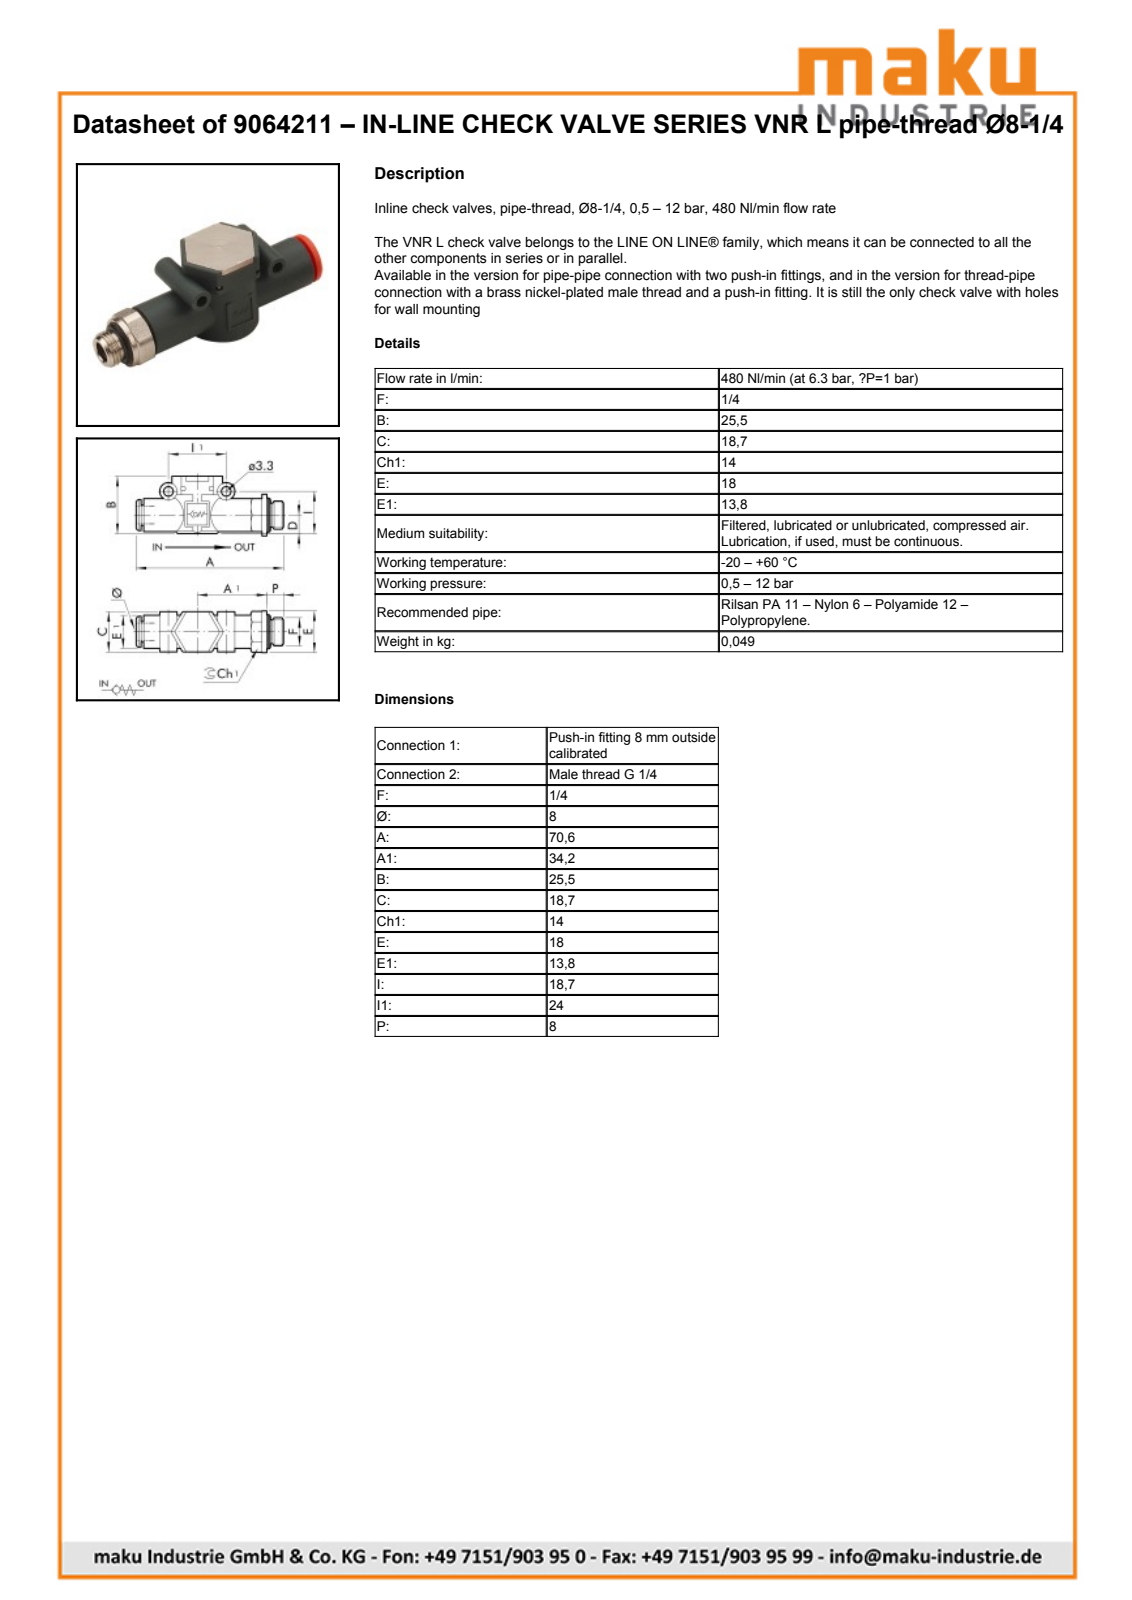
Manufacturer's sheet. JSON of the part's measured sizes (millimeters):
{"part_name": "9064211; LINE-ON-LINE D8 VSR-L body; LINE-ON-LINE D8-1/4 thread port; LINE-ON-LINE D8 VNR-L bushing (+1 more)", "step_written_by": "PARTsolutions (AUTOMOTIVE_DESIGN)", "units": "millimeters", "bodies": {"solids": 4, "faces": 148, "planar": 86, "cylindrical": 51, "other": 11}, "overall_size": [70.8, 26, 18.7], "volume_mm3": 9782, "surface_area_mm2": 10088, "round_holes": [[3.3, 2], [6, 2], [5.5, 1], [8, 1], [8.1, 1], [9.4, 1], [11, 1], [11.66, 1], [12.5, 1], [15, 1]], "round_bosses_or_shafts": [[6, 2], [18.8, 1], [18, 1], [13.8, 1], [13.6, 1], [13.16, 1], [11.1, 1], [10, 1]], "partial_cylinders_radius": [[3.75, 1], [7.95, 1], [10.2, 1], [10.35, 1], [11.45, 1]], "face_to_face_distances": [1.9, 24.1, 26, 4.1, 20, 21.9, 2, 0.94, 49.06, 13.8], "hole_center_spacings": [15.37, 24]}
